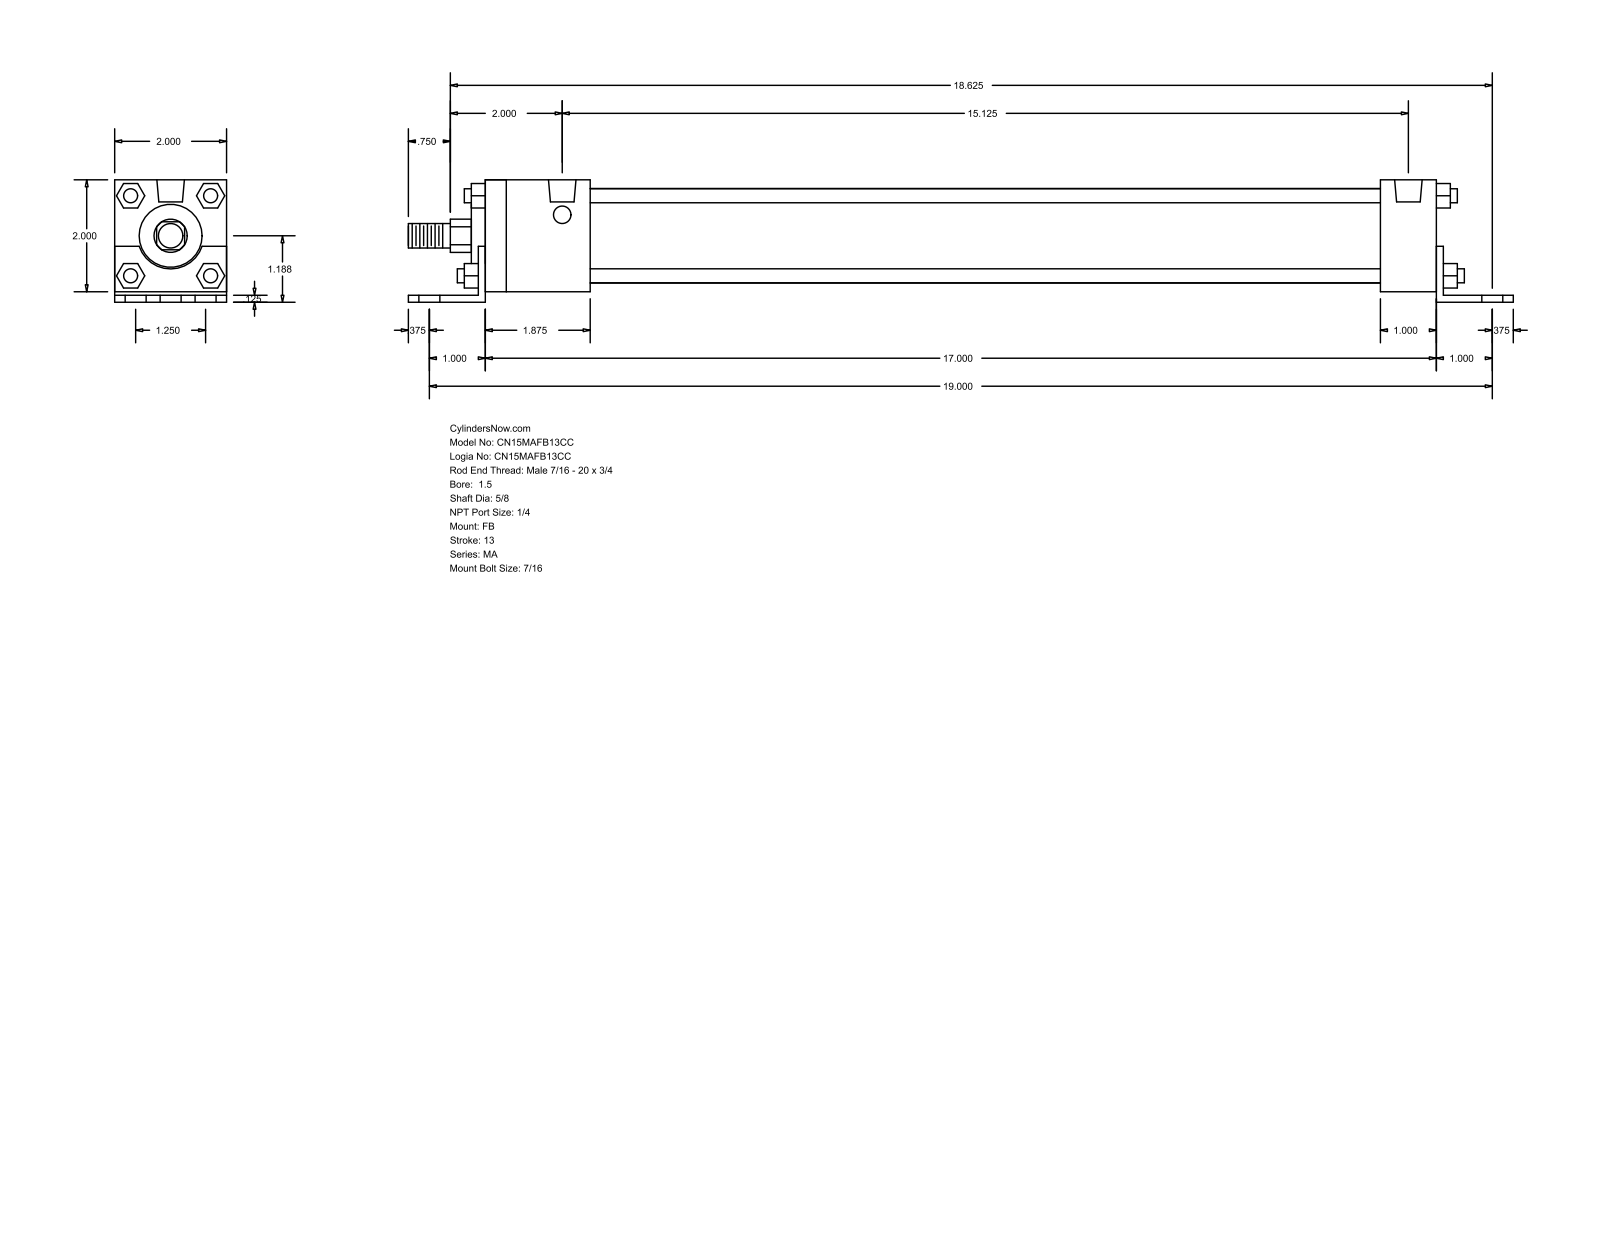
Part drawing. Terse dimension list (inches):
name: MA_FB__0150_0.625
written by: GSSL Pune (CONFIG_CONTROL_DESIGN)
unit: in
bodies: 0 solids, 140 faces (105 planar, 35 cylindrical, 0 other)
size: 19.75 × 2.187 × 2
holes: 6× ⌀0.437, 4× ⌀0.313, 2× ⌀0.492
bosses: 4× ⌀0.25, 1× ⌀1.69, 1× ⌀1.125, 1× ⌀0.625, 1× ⌀0.437
rounds: 1× R0.297, 1× R0.593
face distances: 2, 0.125, 0.187, 2.187, 0.063, 2.063, 1.125, 17.25, 0.125, 17.375
hole spacings: 0.625, 19.01, 19, 1.25, 1.625, 2.456, 15.125, 16.637
